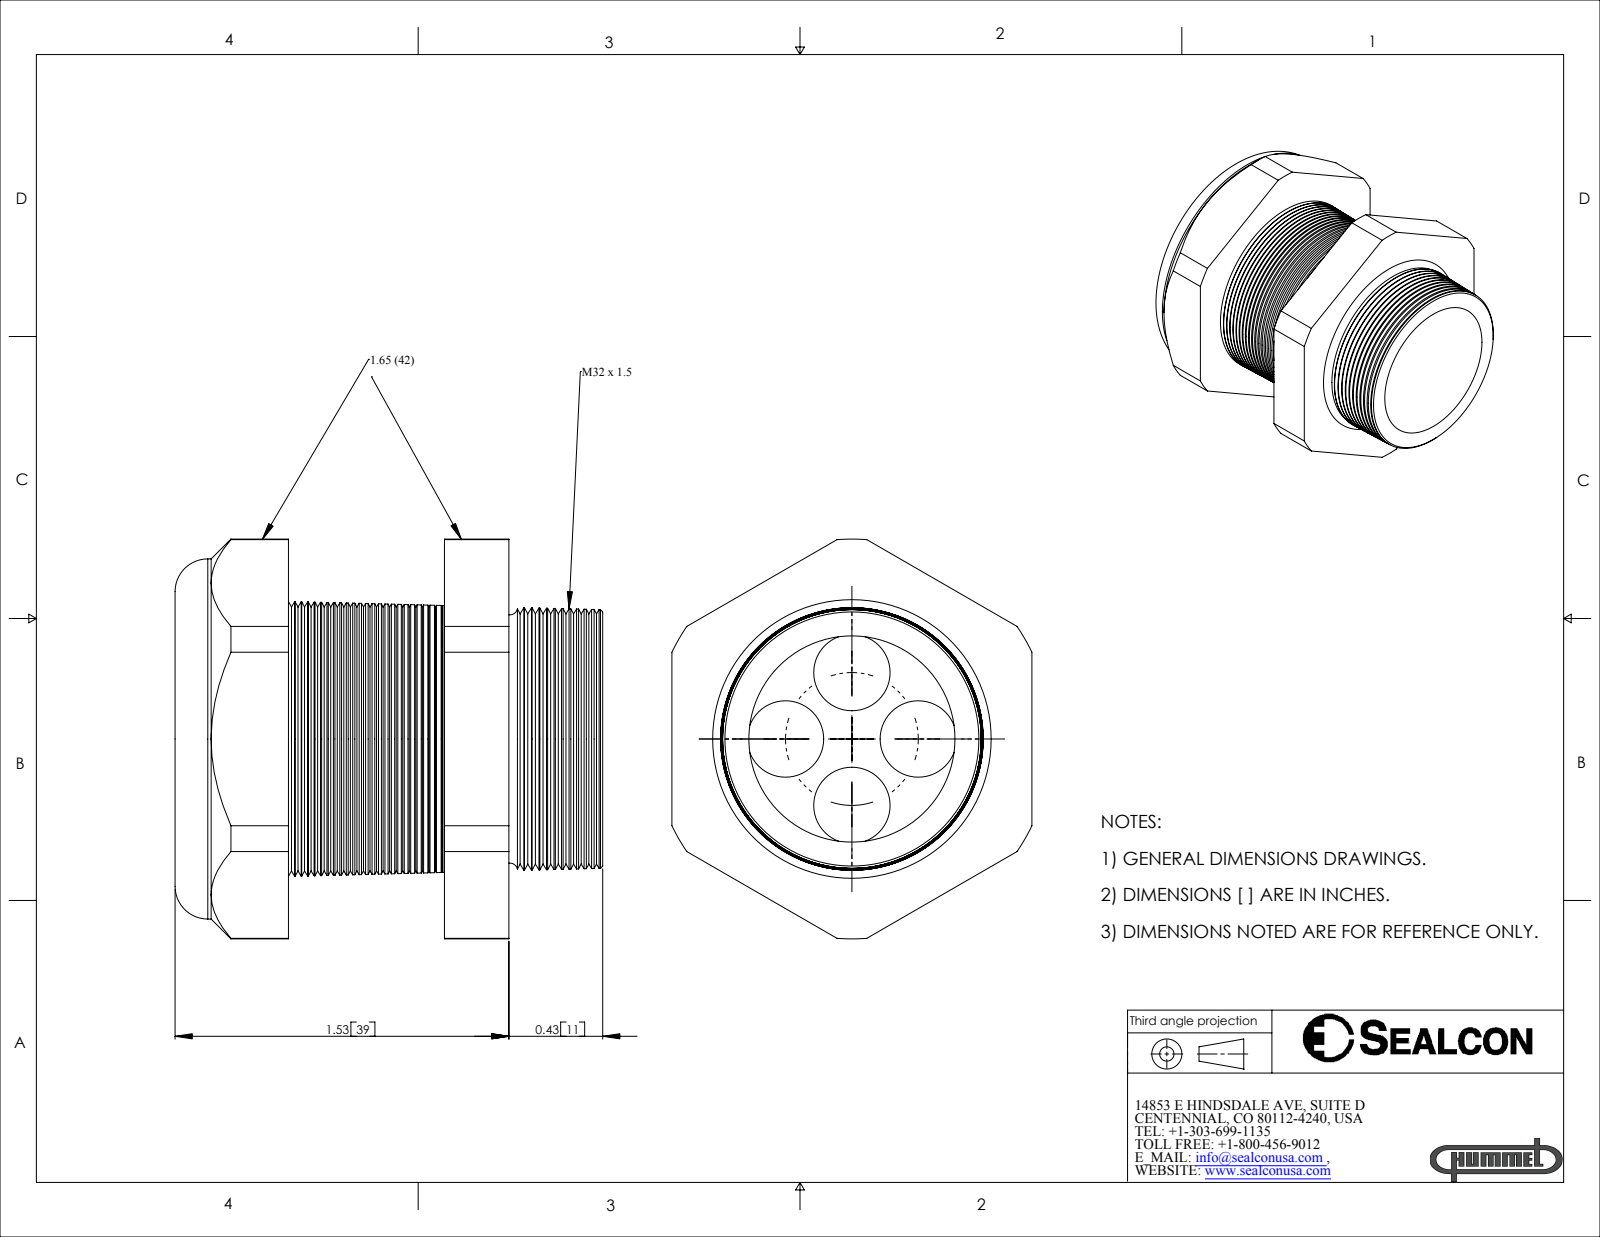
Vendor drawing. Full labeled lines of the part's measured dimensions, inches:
Part name (STEP PRODUCT): CD32M2-GY
STEP written by: SolidWorks 2007 (CONFIG_CONTROL_DESIGN)
Units: inches
Bodies: 2 solids, 279 faces (21 planar, 28 cylindrical, 230 other)
Overall size (bounding box): 1.96 × 1.831 × 1.65
Volume: 1.891 in³ · Surface area: 27.34 in²
Round holes (diameter × count): ⌀0.35 ×4, ⌀0.96 ×1, ⌀0.98 ×1
Round bosses / shafts (diameter × count): ⌀1.65 ×1
Partial cylindrical surfaces — rounded edges, fillets, slot ends (radius × count): R0.916 ×1
Main face-to-face distances: 0.715, 1.011, 0.295, 1.65, 0.52, 1.235, 1.53, 1.65, 0.5, 0.02
Hole centre spacings: 0.304, 0.43, 0.609
